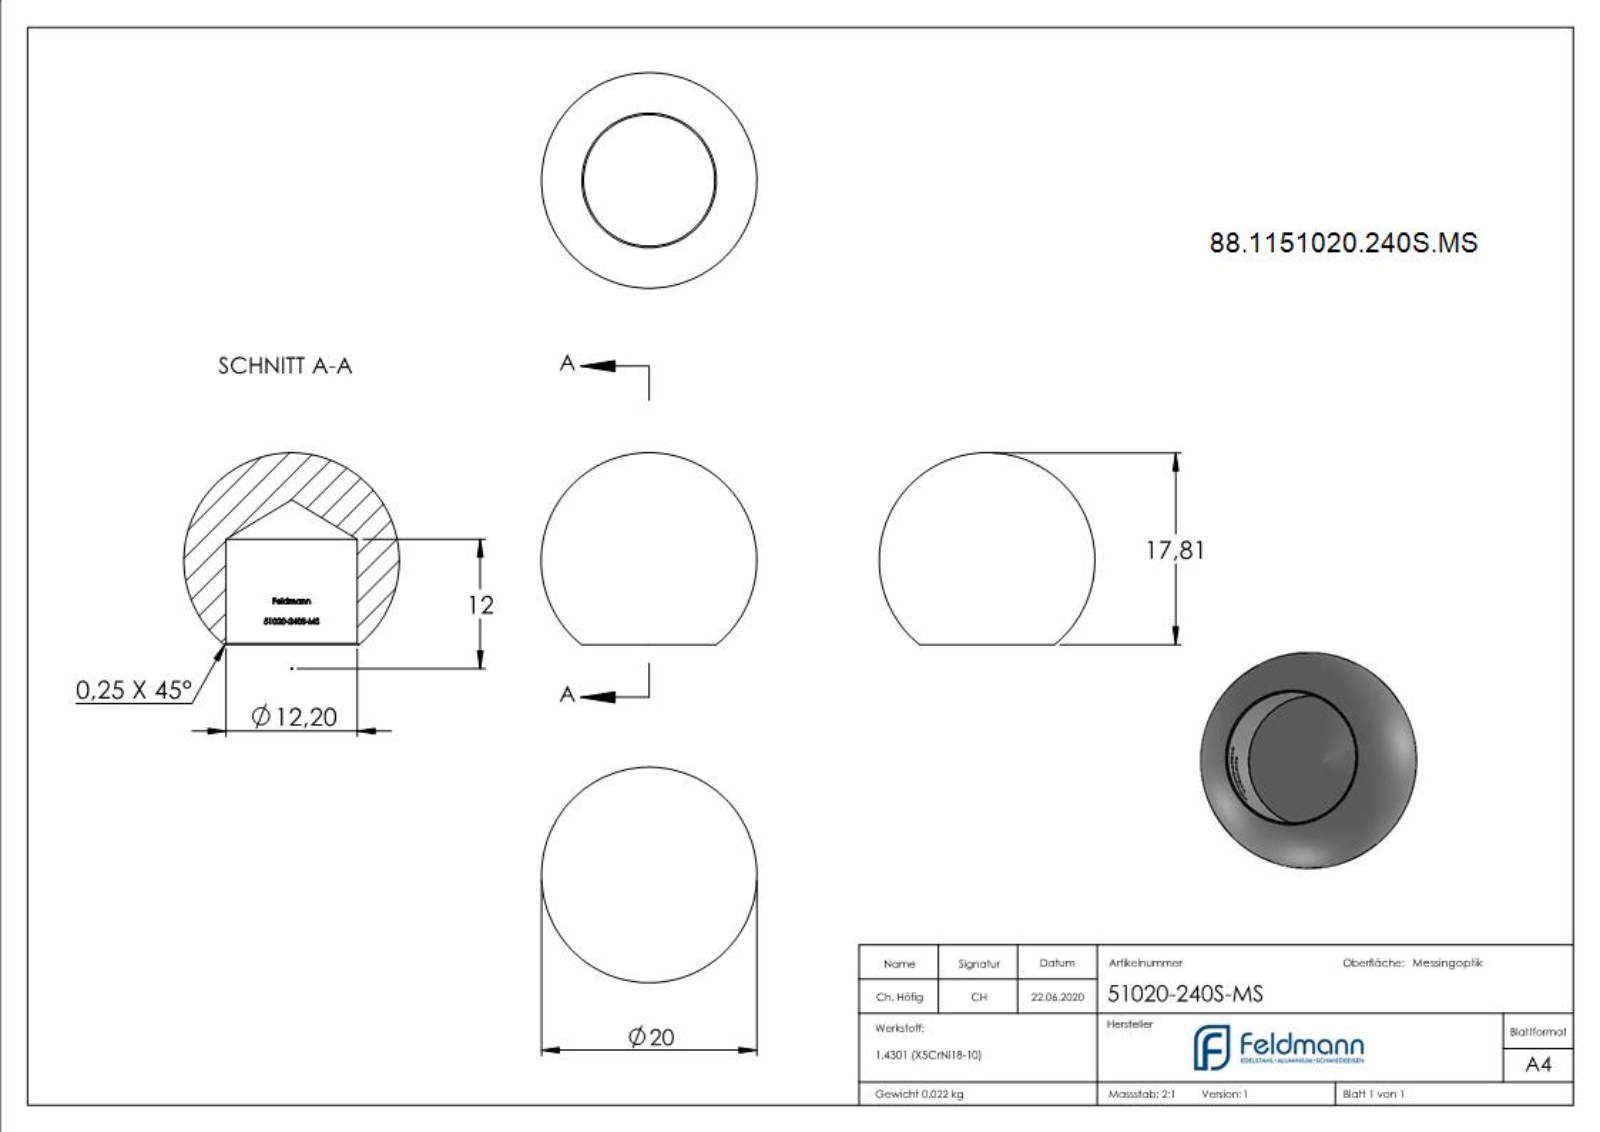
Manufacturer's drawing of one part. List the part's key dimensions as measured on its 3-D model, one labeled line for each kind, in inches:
Part name (STEP PRODUCT): 51020-240S-MS
STEP written by: SolidWorks 2015 (CONFIG_CONTROL_DESIGN)
Units: inches
Bodies: 1 solid, 273 faces (116 planar, 29 cylindrical, 128 other)
Overall size (bounding box): 0.787 × 0.787 × 0.701
Volume: 0.168 in³ · Surface area: 2.54 in²
Round holes (diameter × count): ⌀0.48 ×1
Partial cylindrical surfaces — rounded edges, fillets, slot ends (radius × count): R0.244 ×1
Main face-to-face distances: 0.047, 0.074, 0.053, 0.072, 0.062, 0.026, 0.021, 0.084, 0.022, 0.043
